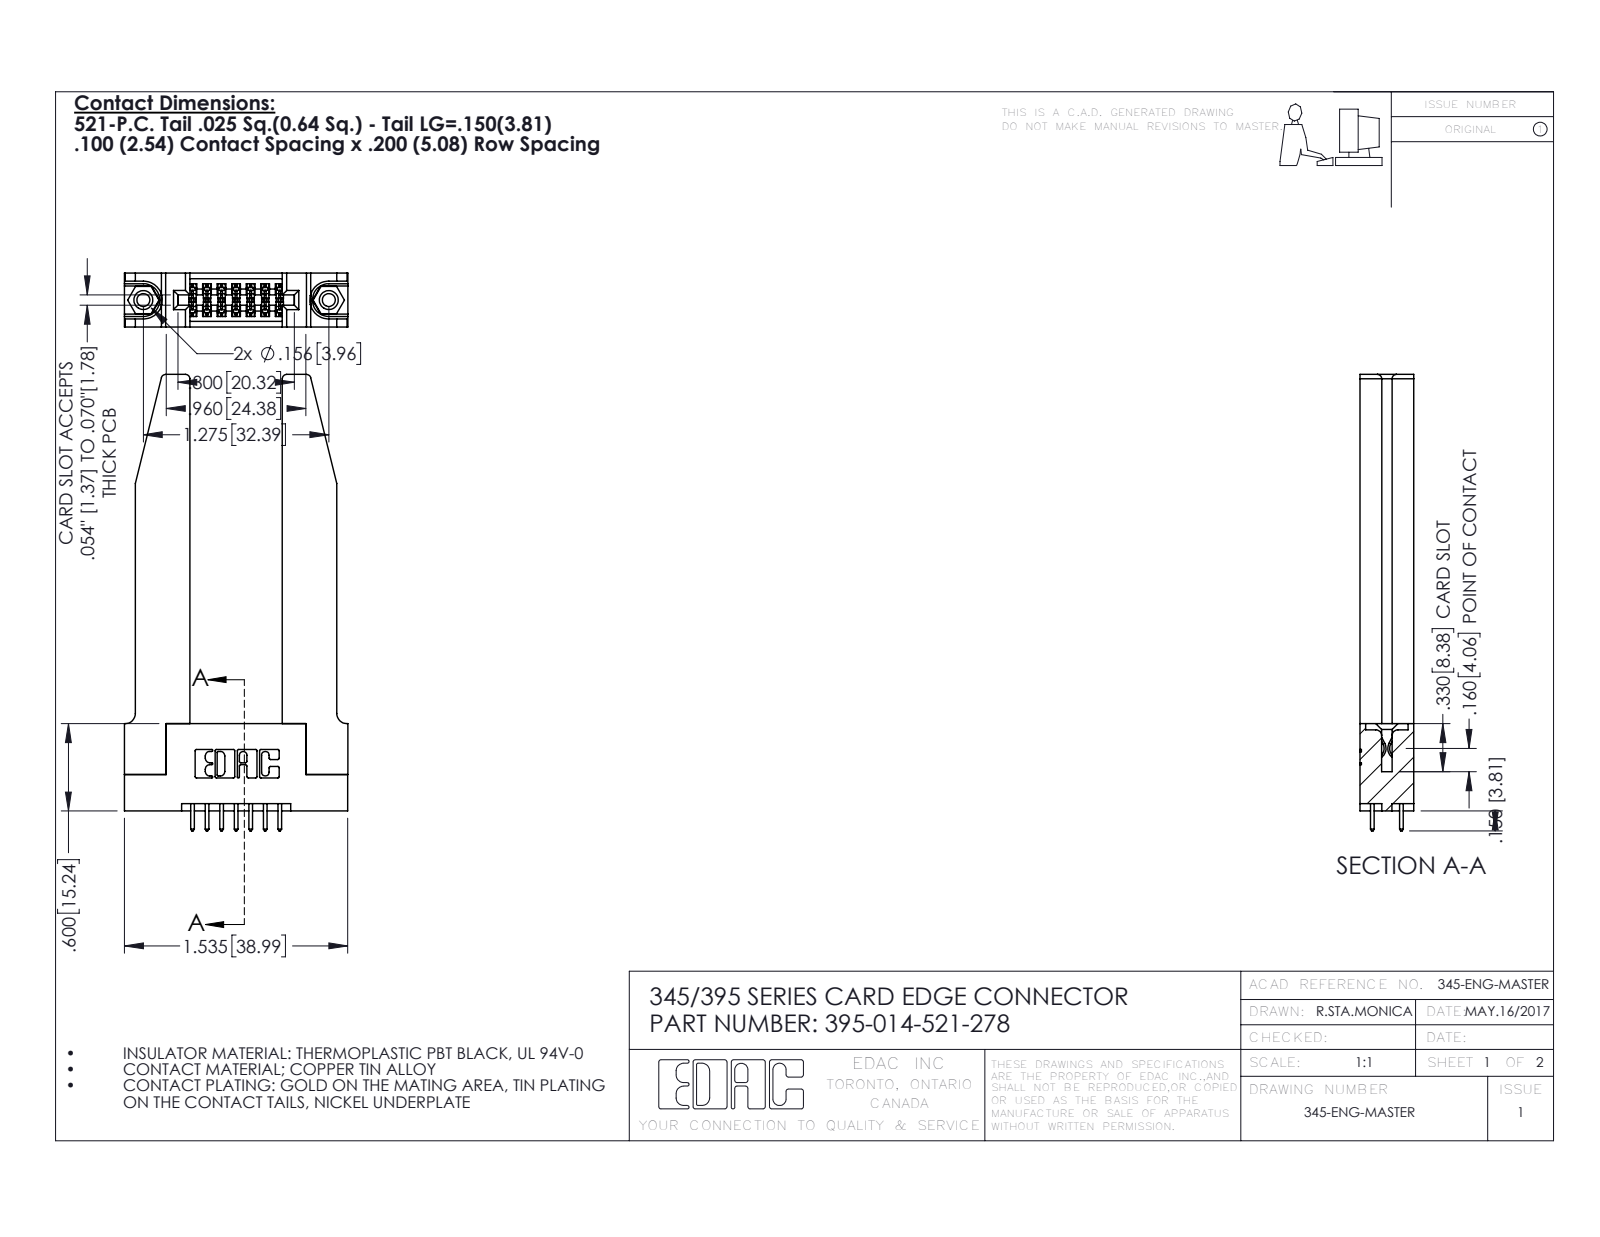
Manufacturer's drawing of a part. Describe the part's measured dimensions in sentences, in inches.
The part is named "345-292-001_345-293-121; 345-220-078_345-220-078; 395-014-521-278; 345 Part_Flush Mounting Lugs - 0.156 Dia-TH (+1 more)". Its 3-D file was written by "SolidWorks 2016 (CONFIG_CONTROL_DESIGN)". It is 19 solids with 1060 faces: 684 planar, 324 cylindrical and 52 other. Overall it measures 3.137 by 1.536 by 0.37 inches. Its volume is 0.685 cubic inches and its surface area 17.42 square inches. Round holes: 2 of diameter 0.089, 2 of diameter 0.125, 2 of diameter 0.156, 1 of diameter 0.064. Round bosses or shafts: 2 of diameter 0.155. Partial cylindrical surfaces (rounded edges, fillets, slot ends): 22 of radius 0.01, 21 of radius 0.006, 14 of radius 0.01, 8 of radius 0.03, 6 of radius 0.007, 6 of radius 0.031, 3 of radius 0.026, 2 of radius 0.014. The main face-to-face distances are 0.37, 0.072, 0.15, 0.148, 0.298, 0.077, 0.22, 0.635, 0.2, 0.095. The hole center spacings are 0.27, 1.045, 1.275.
